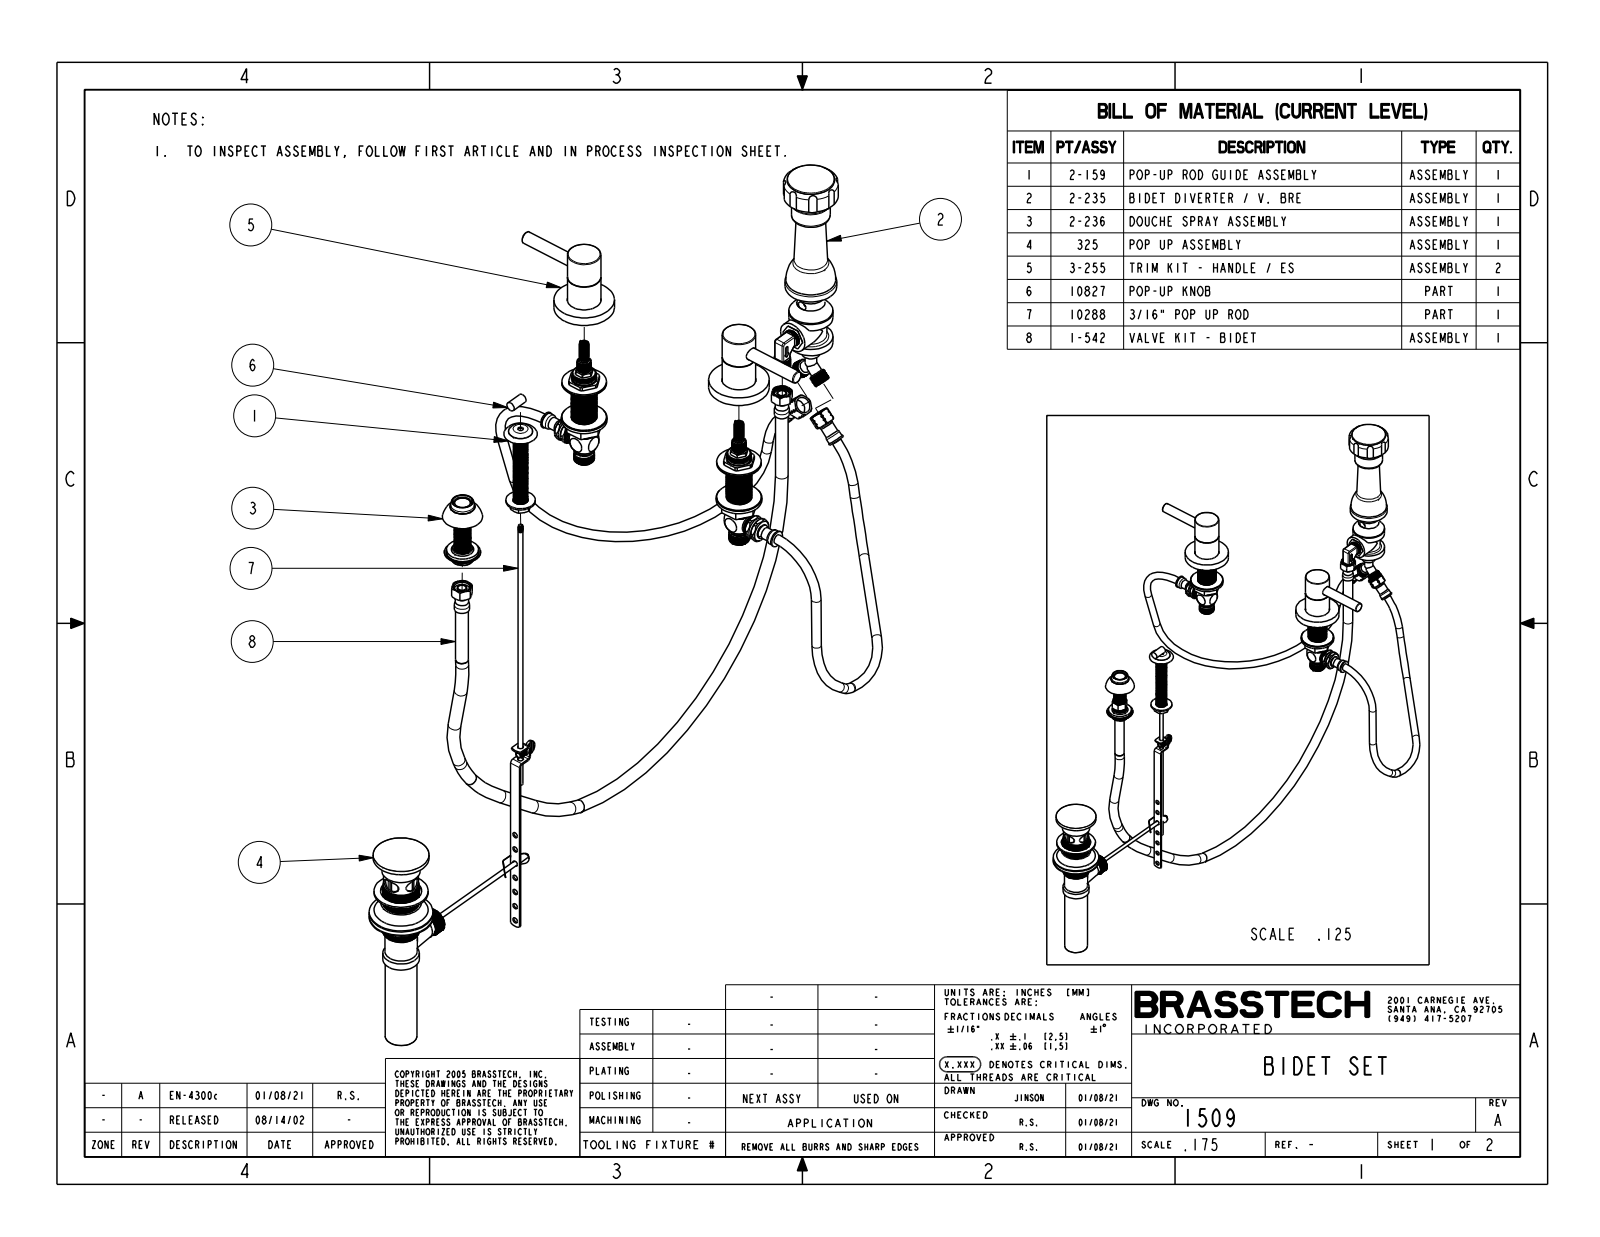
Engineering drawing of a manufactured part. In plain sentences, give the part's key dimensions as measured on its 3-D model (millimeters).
The part is named "1509". Its 3-D file was written by "CREO PARAMETRIC BY PTC INC, 2018400 (CONFIG_CONTROL_DESIGN)". It is 5 solids with 166 faces: 50 planar, 62 cylindrical and 54 other. Overall it measures 580.5 by 355.9 by 136 millimeters. Its volume is 366 100 cubic millimeters and its surface area 65 480 square millimeters. Round holes: 1 of diameter 15.9, 1 of diameter 20.1, 1 of diameter 23.9. Round bosses or shafts: 2 of diameter 60.3, 2 of diameter 33.4, 2 of diameter 33.3, 2 of diameter 10.2, 1 of diameter 51.4, 1 of diameter 38.6, 1 of diameter 23.5, 1 of diameter 19.7. Partial cylindrical surfaces (rounded edges, fillets, slot ends): 8 of radius 5.3, 1 of radius 9.1, 1 of radius 27.4. The main face-to-face distances are 9.5, 28.1, 0.5, 66.6, 57.1, 37.7, 29, 38.2, 28.7, 28.4.
